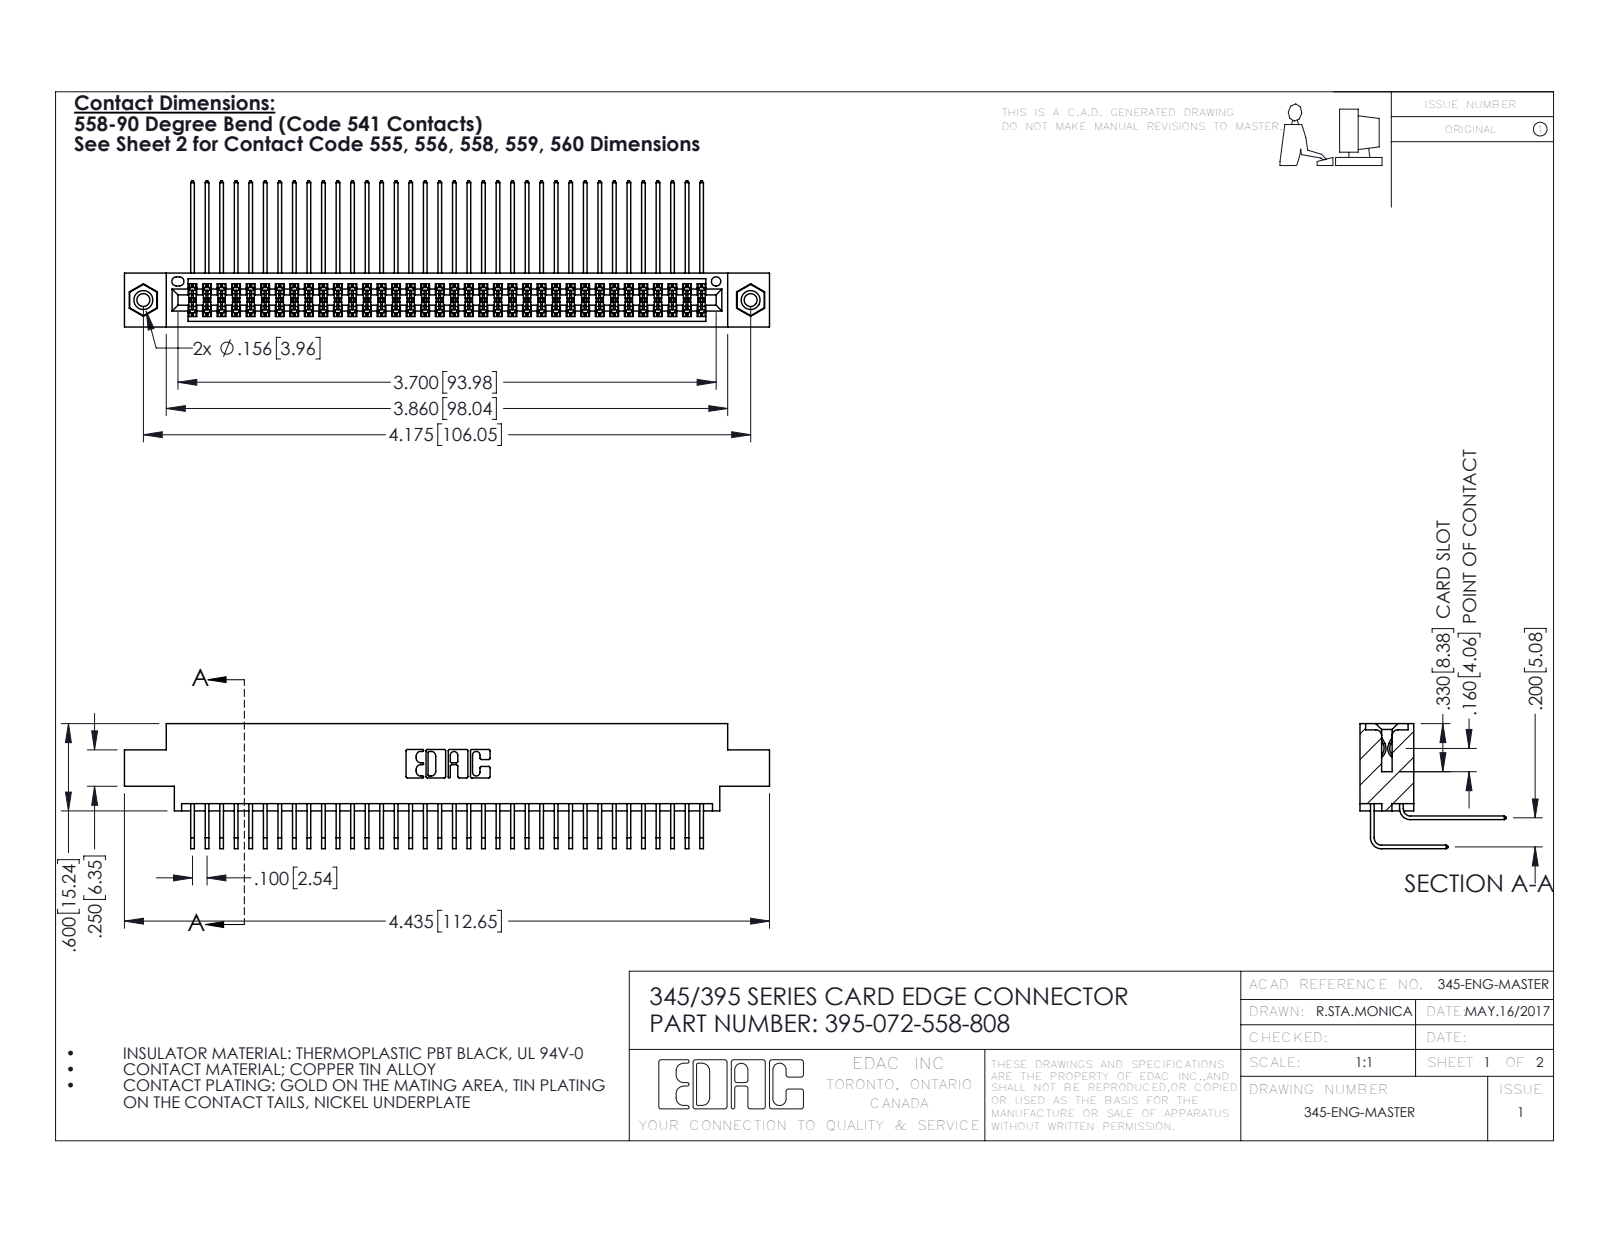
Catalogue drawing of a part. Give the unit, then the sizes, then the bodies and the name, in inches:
Units: inches
Overall size (bounding box): 4.435 × 1.005 × 0.859
Round holes (diameter × count): ⌀0.089 ×2, ⌀0.125 ×2, ⌀0.156 ×2, ⌀0.064 ×1
Round bosses / shafts (diameter × count): ⌀0.155 ×2
Partial cylindrical surfaces — rounded edges, fillets, slot ends (radius × count): R0.006 ×109, R0.01 ×22, R0.007 ×6, R0.031 ×6, R0.026 ×3, R0.014 ×2, R0.019 ×2, R0.022 ×2
Main face-to-face distances: 0.072, 0.298, 0.2, 0.37, 0.098, 0.272, 0.025, 0.225, 0.175, 0.025
Hole centre spacings: 0.27, 3.939, 4.175
Volume: 0.682 in³ · Surface area: 28.71 in²
Bodies: 75 solids, 3934 faces (2636 planar, 1282 cylindrical, 16 other)
Part name (STEP PRODUCT): 345-292-001_558 Tail - 2; 345 Part_0.170 Offset - 0.156 Dia-TI; 345-250-001_345-250-003-102; 345-292-001_558 559 Tail - 1 (+1 more)
STEP written by: SolidWorks 2016 (CONFIG_CONTROL_DESIGN)
